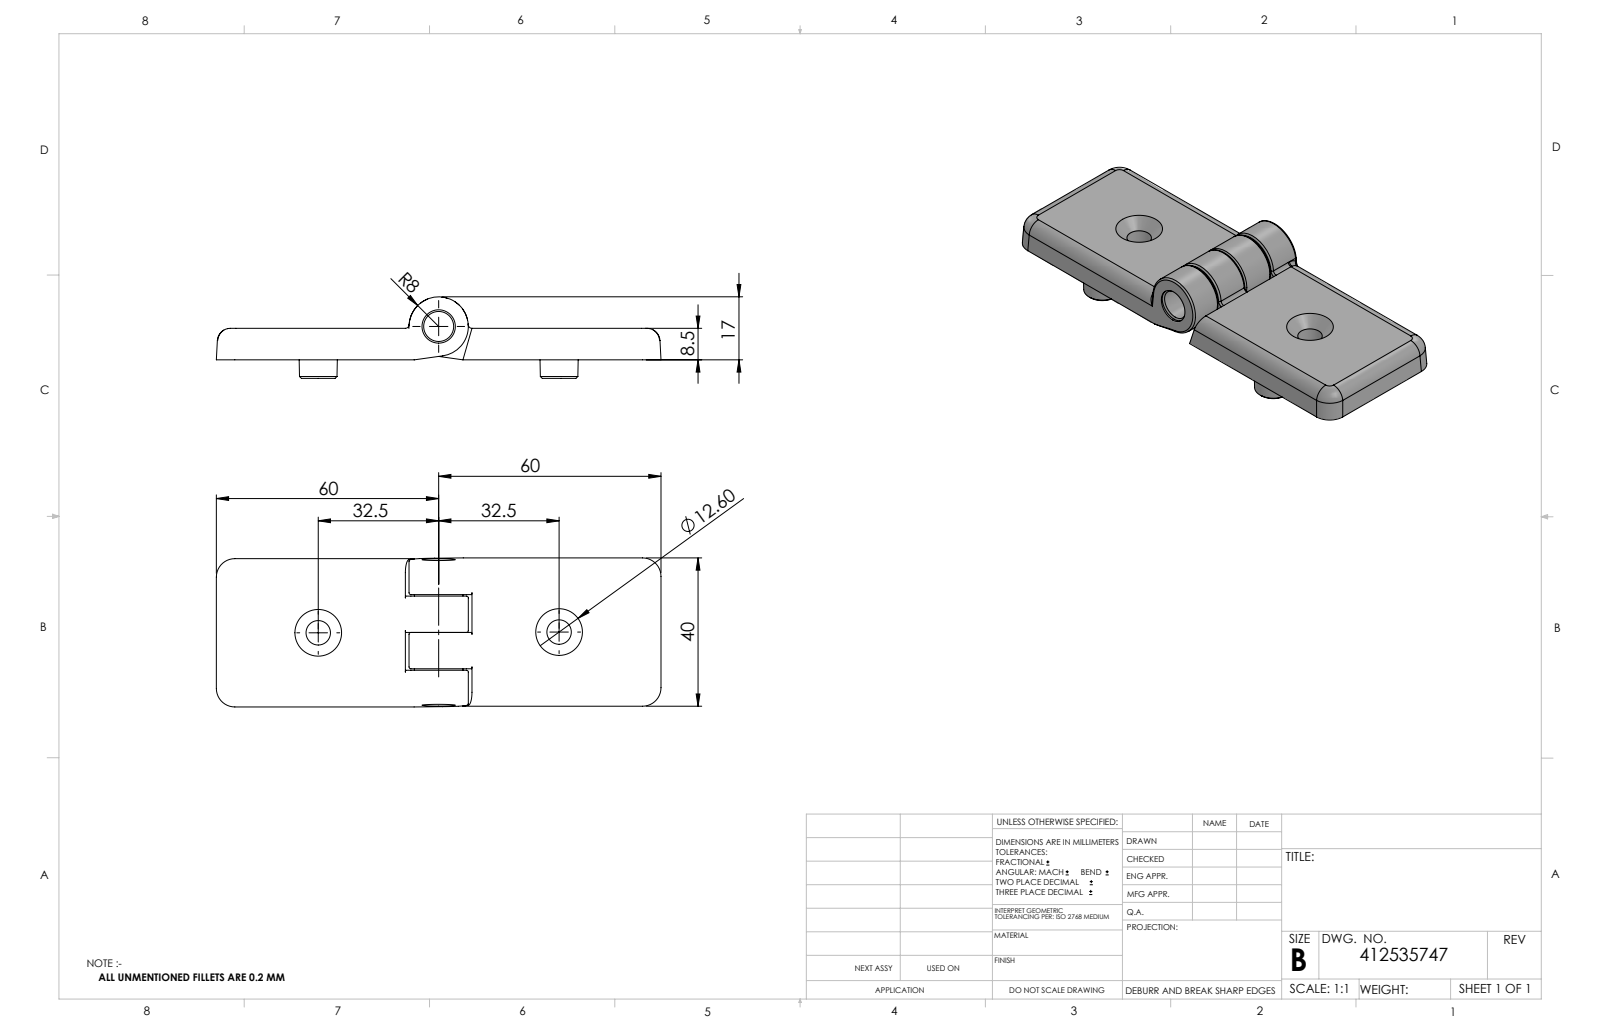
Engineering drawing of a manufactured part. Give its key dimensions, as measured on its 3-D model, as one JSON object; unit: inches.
{"part_name": "412535747_c_1", "step_written_by": "SolidWorks 2014 (CONFIG_CONTROL_DESIGN)", "units": "inches", "bodies": {"solids": 11, "faces": 768, "planar": 201, "cylindrical": 250, "other": 317}, "overall_size": [4.724, 1.583, 1.028], "volume_in3": 2.127, "surface_area_in2": 36.4, "round_holes": [[0.197, 2], [0.26, 2], [0.319, 1], [0.354, 1]], "round_bosses_or_shafts": [[0.446, 2], [0.236, 2], [0.63, 1], [0.323, 1], [0.315, 1]], "partial_cylinders_radius": [[0.02, 58], [0.039, 14], [0.008, 12], [0.079, 8], [0.138, 6], [0.106, 4], [0.122, 4], [0.197, 4]], "face_to_face_distances": [0.197, 0.335, 0.138, 0.016, 0.386, 0.402, 0.787, 0.161, 0.394, 0.531], "hole_center_spacings": [2.559]}
